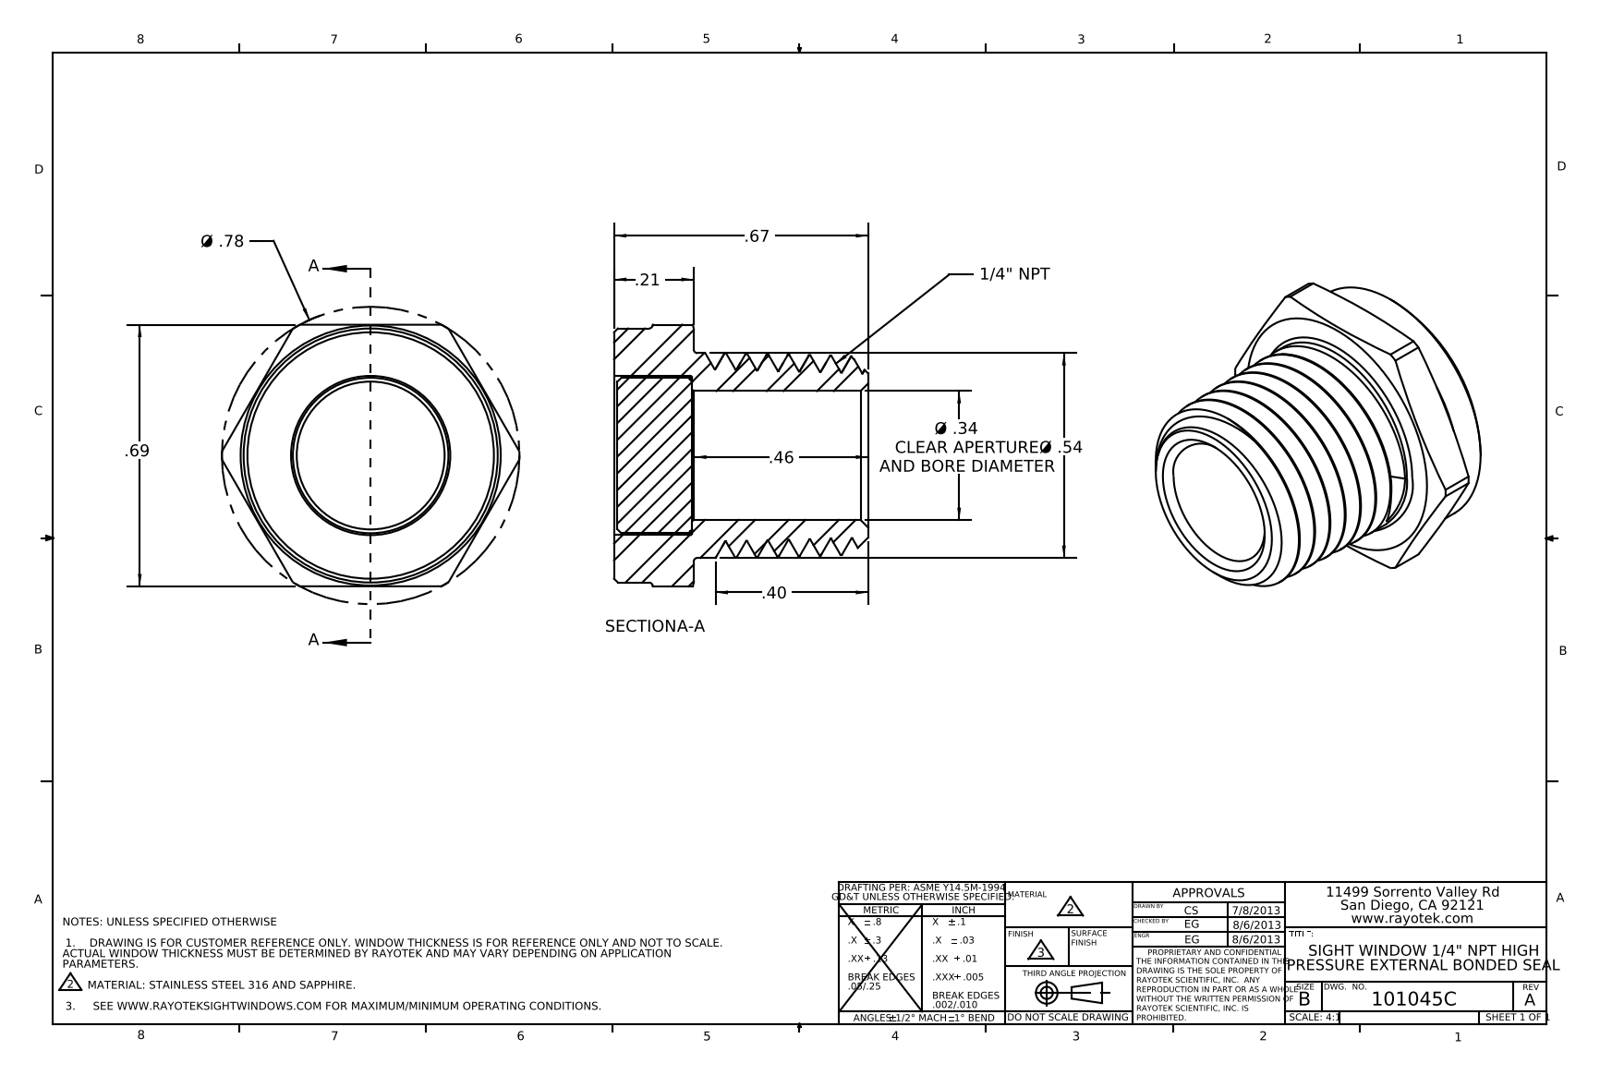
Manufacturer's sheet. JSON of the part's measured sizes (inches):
{"part_name": "101045; 402045; 403045", "step_written_by": "SolidWorks 2012 (AUTOMOTIVE_DESIGN)", "units": "inches", "bodies": {"solids": 2, "faces": 72, "planar": 15, "cylindrical": 18, "other": 39}, "overall_size": [0.785, 0.69, 0.67], "volume_in3": 0.123, "surface_area_in2": 3.508, "round_holes": [[0.34, 1], [0.42, 1]], "round_bosses_or_shafts": [[0.67, 1], [0.54, 1], [0.41, 1]], "partial_cylinders_radius": [[0.392, 1]], "face_to_face_distances": [0.206, 0.197, 0.69, 0.21, 0.201, 0.67, 0.661, 0.464, 0.46]}
